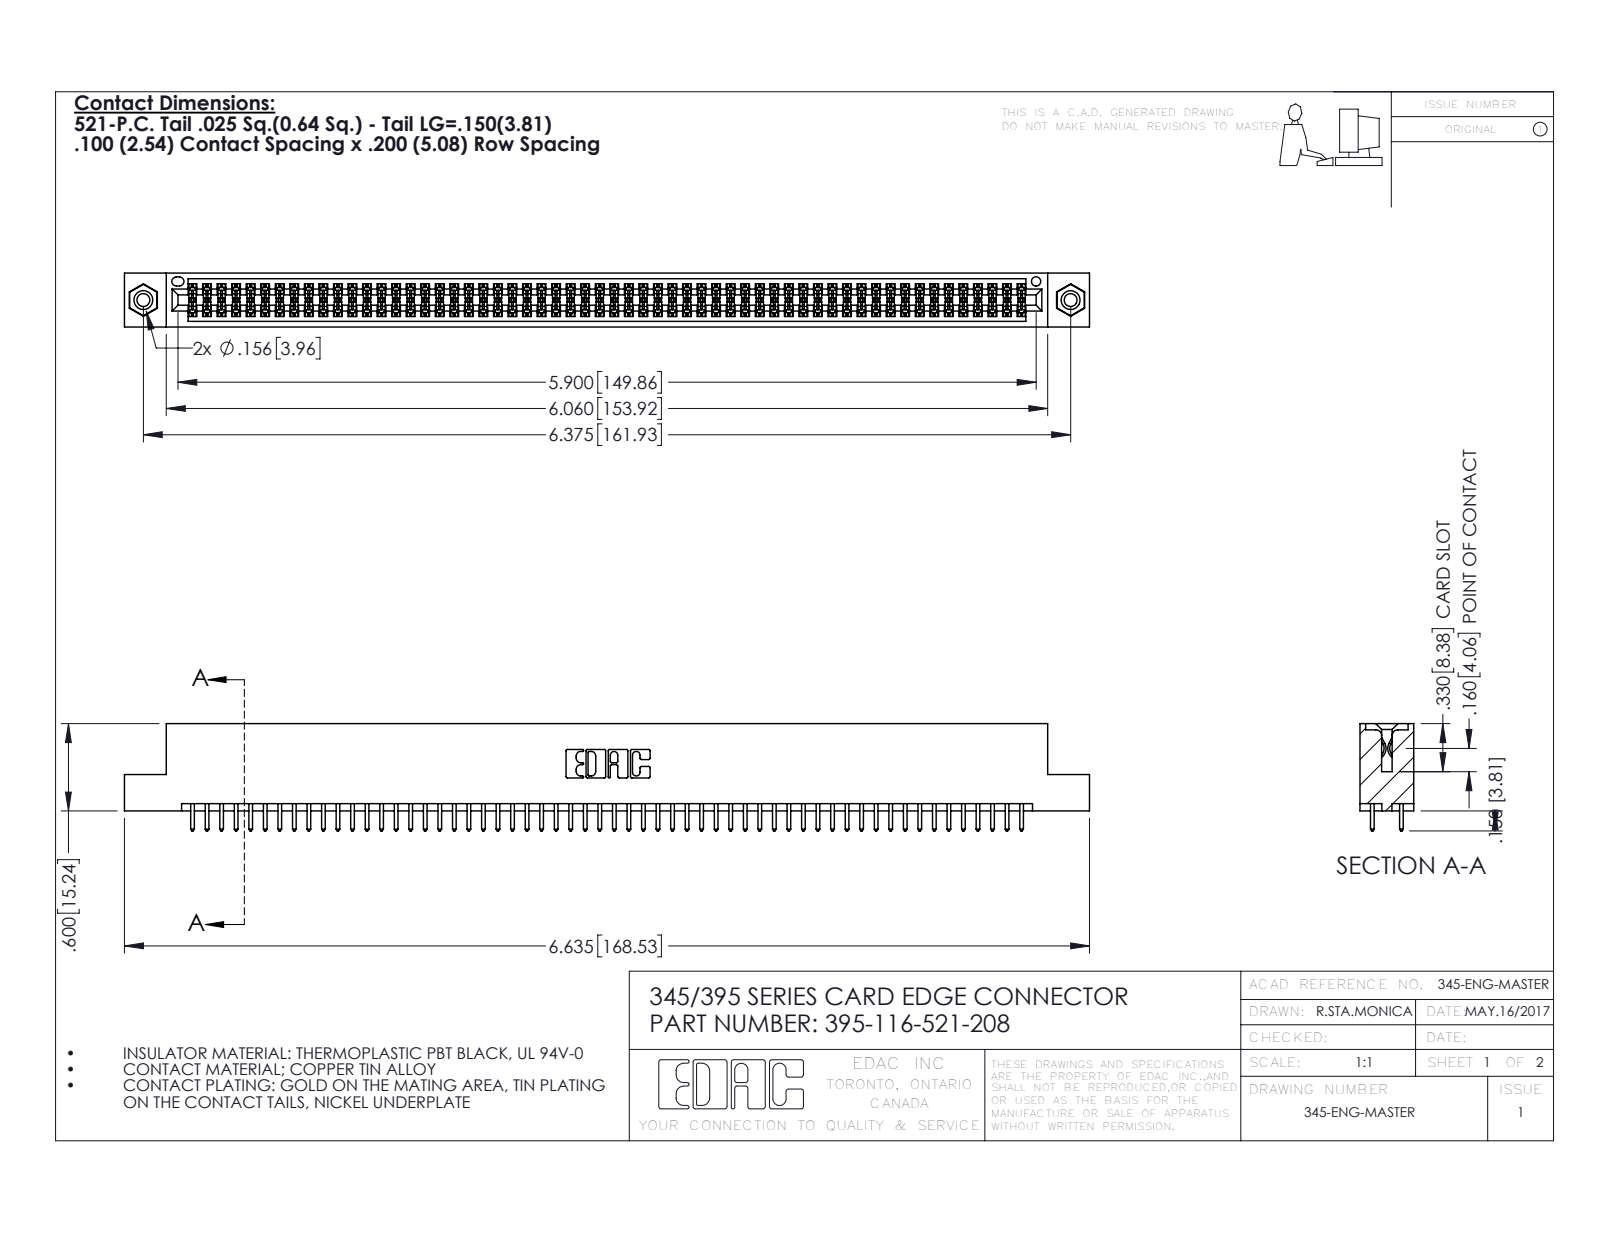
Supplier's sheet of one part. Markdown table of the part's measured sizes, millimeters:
| quantity | value |
| --- | --- |
| part name | 345-250-001_345-250-003-102; 345 Part_Flush Mounting Lugs - 0.156 Dia-TI; 345-292-001_345-293-121; 395-116-521-208 |
| STEP written by | SolidWorks 2016 (CONFIG_CONTROL_DESIGN) |
| units | millimeters |
| bodies | 119 solids, 5986 faces (3940 planar, 2030 cylindrical, 16 other) |
| overall size | 168.5 × 18.7 × 9.4 |
| volume | 16 470 mm³ |
| surface area | 24 350 mm² |
| round holes (diameter × count) | 2.3 × 2, 3.2 × 2, 4 × 2, 1.6 × 1 |
| round bosses / shafts (diameter × count) | 3.9 × 2 |
| partial cylindrical surfaces (radius × count) | 0.2 × 174, 0.3 × 116, 0.3 × 22, 0.2 × 6, 0.8 × 6, 0.7 × 3, 0.4 × 2, 0.5 × 2 |
| main face-to-face distances | 1.8, 7.6, 5.1, 2.5, 6.9, 0.6, 9.4, 5.7, 4.4, 3.8 |
| hole center spacings | 6.9, 155.9, 161.9 |
